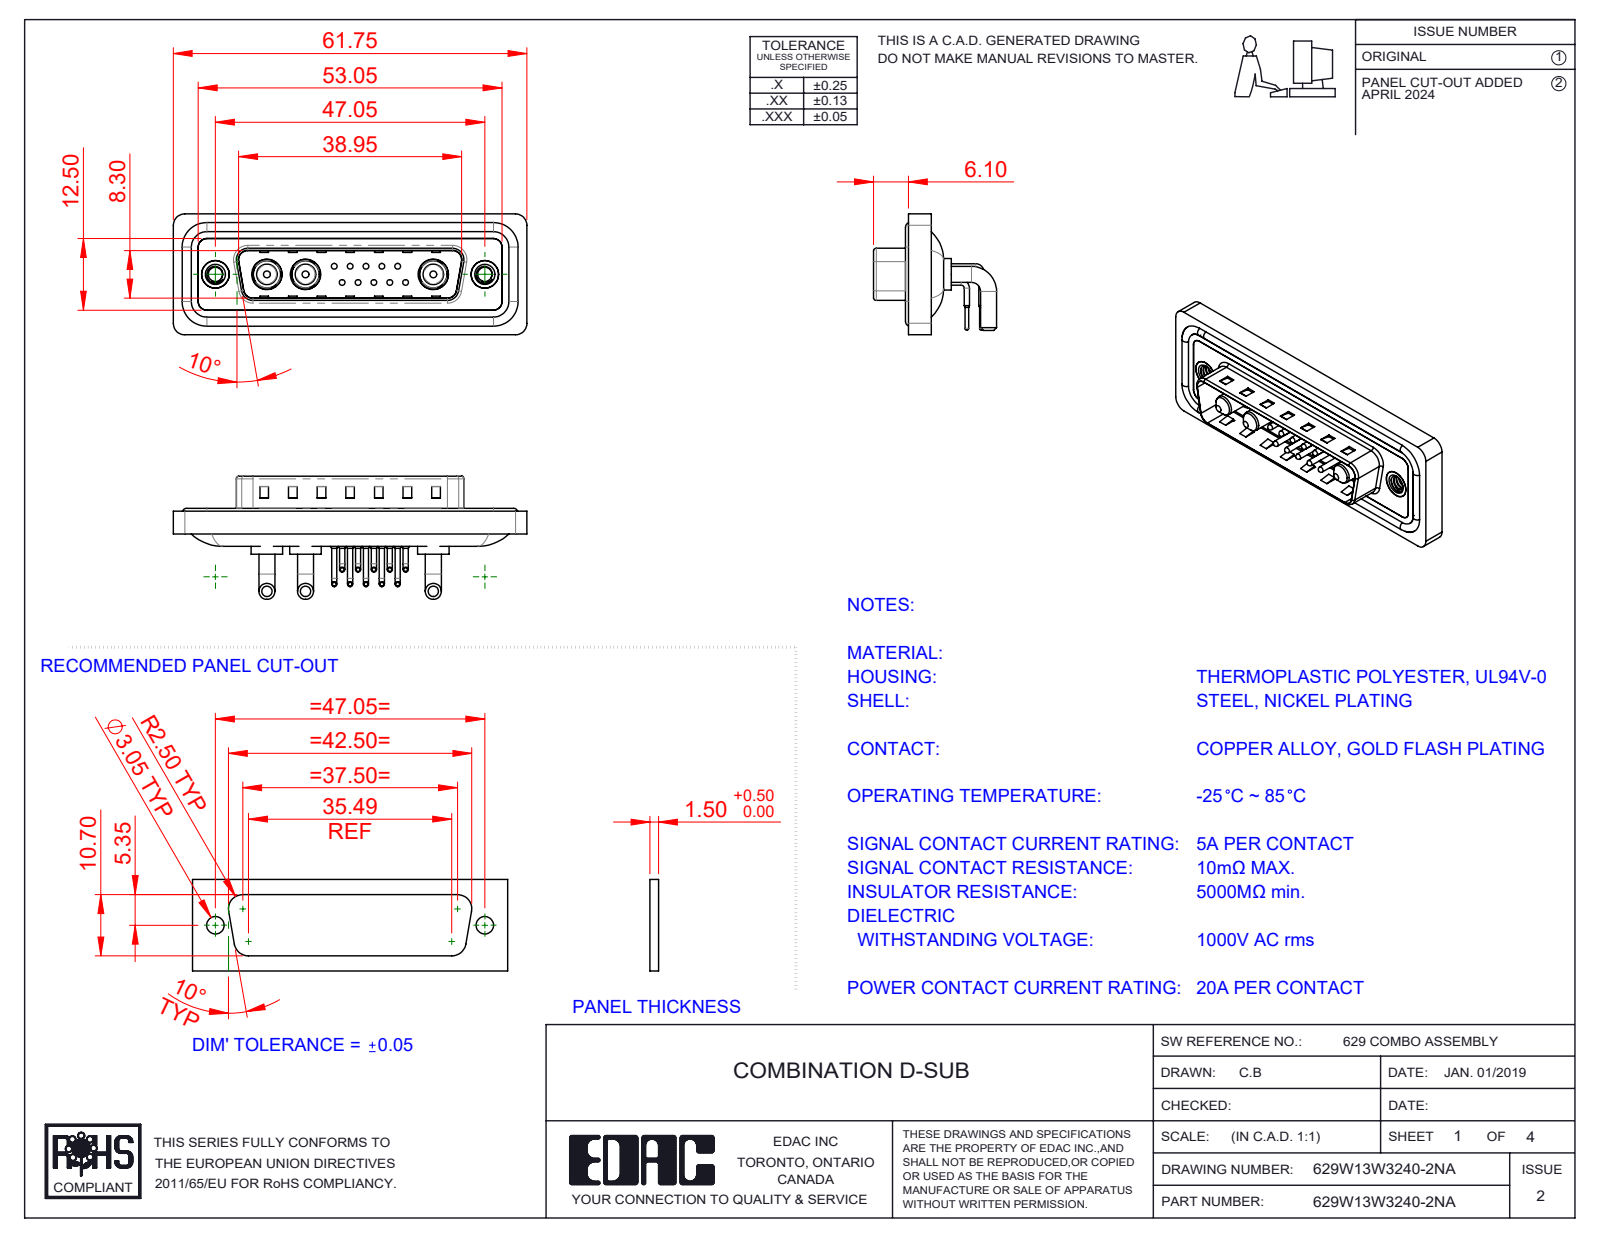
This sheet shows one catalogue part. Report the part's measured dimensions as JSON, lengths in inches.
{"part_name": "629Combo Shell Front_25 Contacts; 629W13W3240-2NA; 629Combo Contact Row 1; 629Combo Waterproof Housing_25 Contacts (+5 more)", "step_written_by": "SolidWorks 2023 (CONFIG_CONTROL_DESIGN)", "units": "inches", "bodies": {"solids": 23, "faces": 1706, "planar": 879, "cylindrical": 609, "other": 218}, "overall_size": [2.431, 0.846, 0.831], "volume_in3": 0.465, "surface_area_in2": 19.38, "round_holes": [[0.03, 10], [0.063, 10], [0.079, 10], [0.191, 3], [0.209, 3], [0.098, 2], [0.157, 2], [0.189, 2], [0.197, 2]], "round_bosses_or_shafts": [[0.035, 20], [0.059, 10], [0.039, 10], [0.026, 10], [0.11, 6], [0.063, 4], [0.217, 3], [0.205, 3]], "partial_cylinders_radius": [[0.059, 18], [0.079, 18], [0.04, 10], [0.02, 8], [0.063, 8], [0.01, 4], [0.024, 4], [0.026, 4]], "face_to_face_distances": [0.016, 0.114, 0.031, 0.161, 0.043, 0.083, 0.063, 0.177, 0.059, 0.236], "hole_center_spacings": [0.124, 0.109, 0.198, 0.218, 0.295, 0.198, 0.327, 0.398]}
